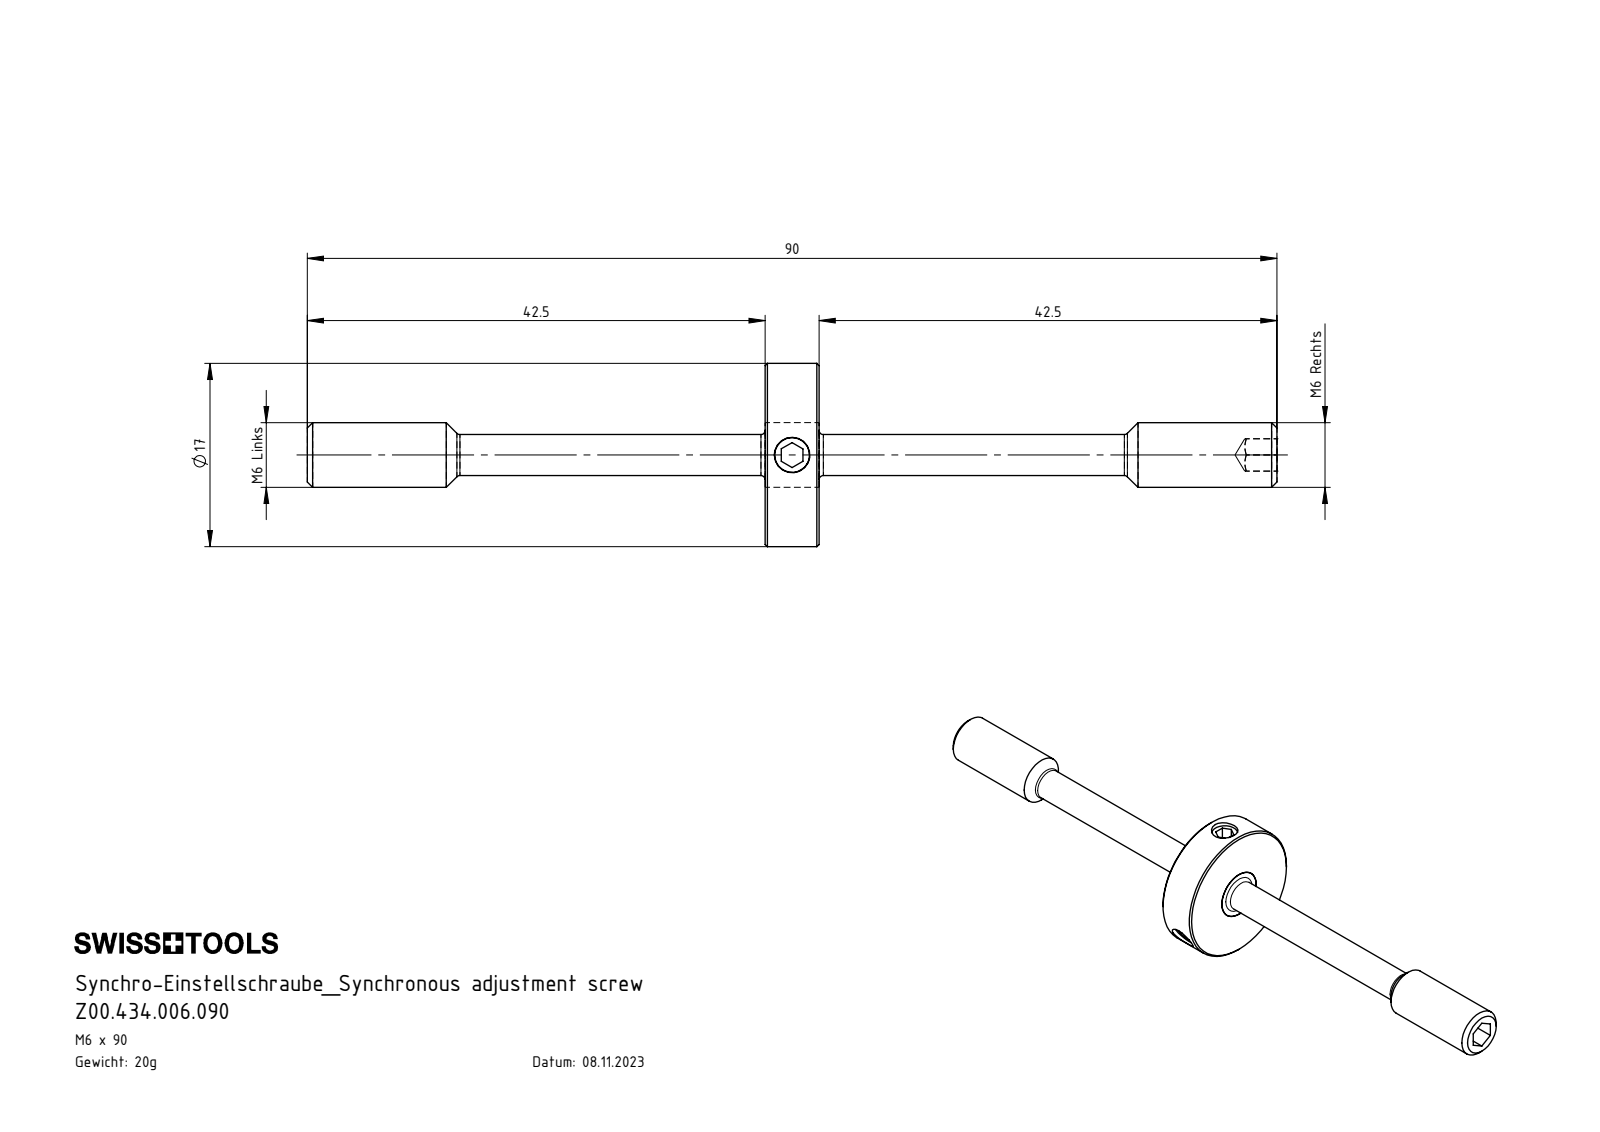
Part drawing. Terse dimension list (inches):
name: Z94-ER3.001.090_A; Z00.434.006.090; Z42-ER3.002.005_A; ISO 4026 - M4 x 5
written by: SolidWorks 2022 (AUTOMOTIVE_DESIGN)
unit: in
bodies: 5 solids, 99 faces (39 planar, 26 cylindrical, 34 other)
size: 3.543 × 0.669 × 0.669
volume: 0.154 in³; area: 3.993 in²
holes: 3× ⌀0.13
bosses: 3× ⌀0.157, 1× ⌀0.669, 1× ⌀0.236, 1× ⌀0.15
face distances: 0.197, 1.673, 1.87, 0.079, 0.098, 0.118, 3.543, 1.732, 1.811, 0.059
